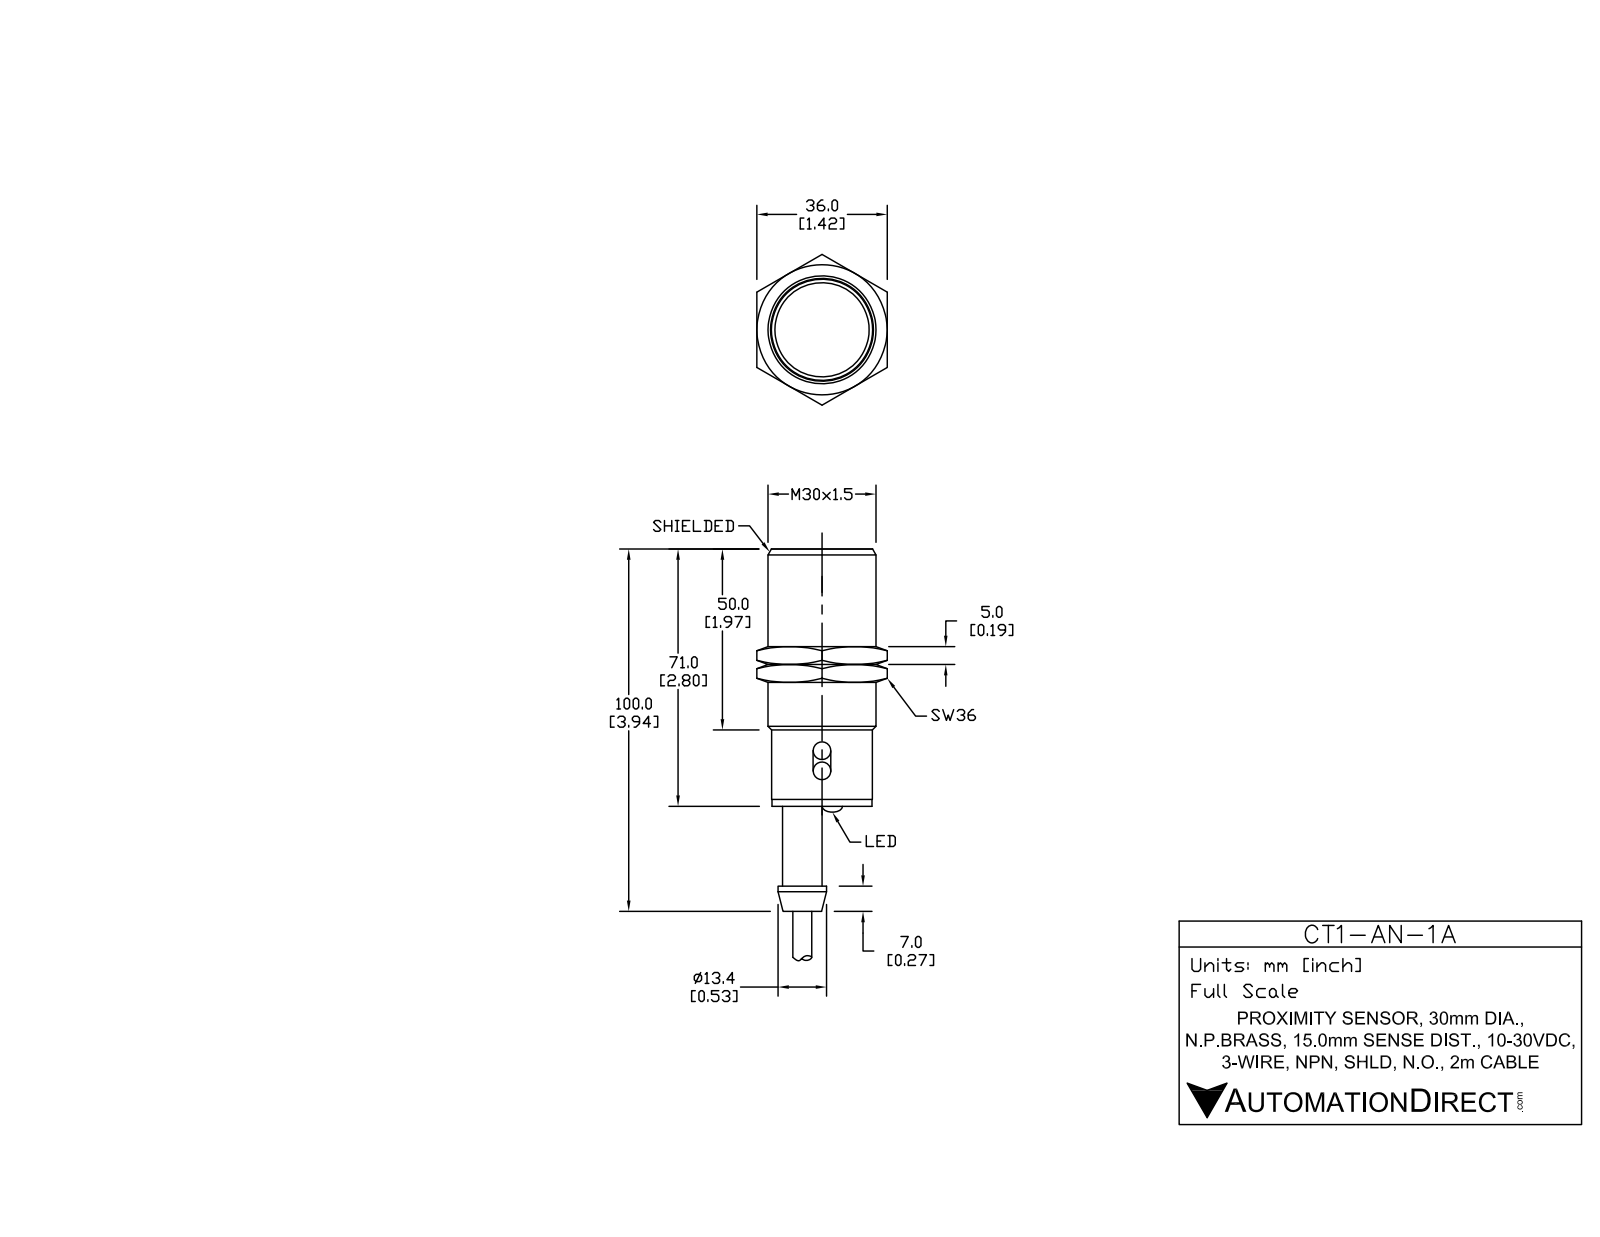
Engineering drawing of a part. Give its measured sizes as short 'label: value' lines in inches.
name: CT1-AN-1A
written by: SolidWorks 2017 (AUTOMOTIVE_DESIGN)
unit: in
bodies: 6 solids, 76 faces (26 planar, 32 cylindrical, 18 other)
size: 4.681 × 1.181 × 1.181
volume: 3.433 in³; area: 24.32 in²
holes: 2× ⌀0.142, 1× ⌀0.205, 1× ⌀0.283, 1× ⌀0.319, 1× ⌀0.413, 1× ⌀1.067
bosses: 2× ⌀0.197, 1× ⌀1.181, 1× ⌀1.098, 1× ⌀1.094, 1× ⌀1.024, 1× ⌀0.433, 1× ⌀0.315
rounds: 2× R0.079
face distances: 2.319, 0.787, 3.106, 3.146, 2.358, 0.039, 3.114, 2.327, 0.031, 0.02
hole spacings: 0.181, 0.264, 0.307, 0.571
